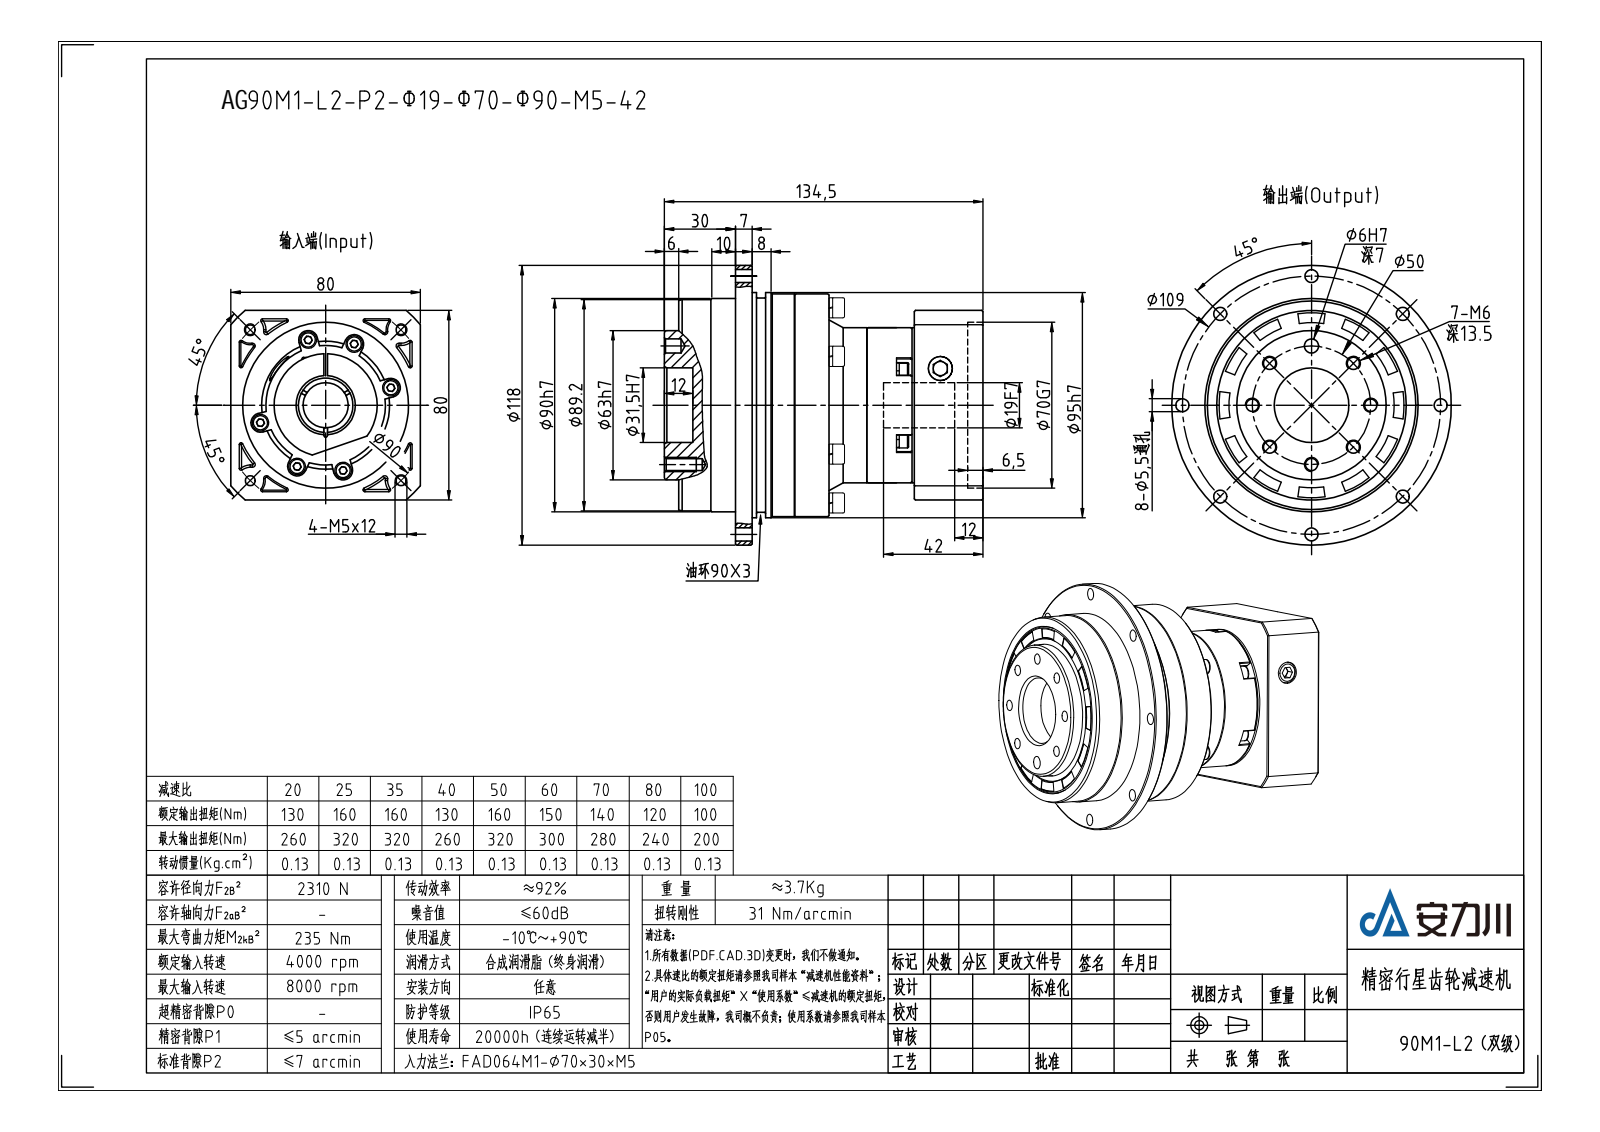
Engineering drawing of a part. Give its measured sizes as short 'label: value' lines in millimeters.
name: 油封63807; 输入太阳齿轮060M1-19; FAD090D-L2-19-70-90-M5-42; 输出内齿圈壳体FAD090D (+8 more)
written by: SolidWorks 2016 (CONFIG_CONTROL_DESIGN)
unit: mm
bodies: 10 solids, 1294 faces (403 planar, 481 cylindrical, 410 other)
size: 134.5 × 118 × 118
volume: 782 187 mm³; area: 156 394 mm²
holes: 15× ⌀5.5, 12× ⌀4.5, 12× ⌀6.2, 10× ⌀4.2, 7× ⌀5, 6× ⌀3.3, 6× ⌀7.8, 1× ⌀3, 1× ⌀4.3, 1× ⌀6, 1× ⌀9, 1× ⌀10.2
bosses: 12× ⌀7, 12× ⌀4.1, 12× ⌀4, 7× ⌀8.5, 7× ⌀5, 6× ⌀5.1, 1× ⌀118, 1× ⌀95
rounds: 12× R0.3, 12× R0.5, 12× R1.73, 12× R4, 3× R37.5, 1× R0.75, 1× R34.85, 1× R39.05
face distances: 69.5, 14, 30.5, 18, 55.5, 25, 7, 16, 39, 79.5
hole spacings: 74.31, 29, 59.96, 36.69, 61.14, 25, 29.5, 40.84
